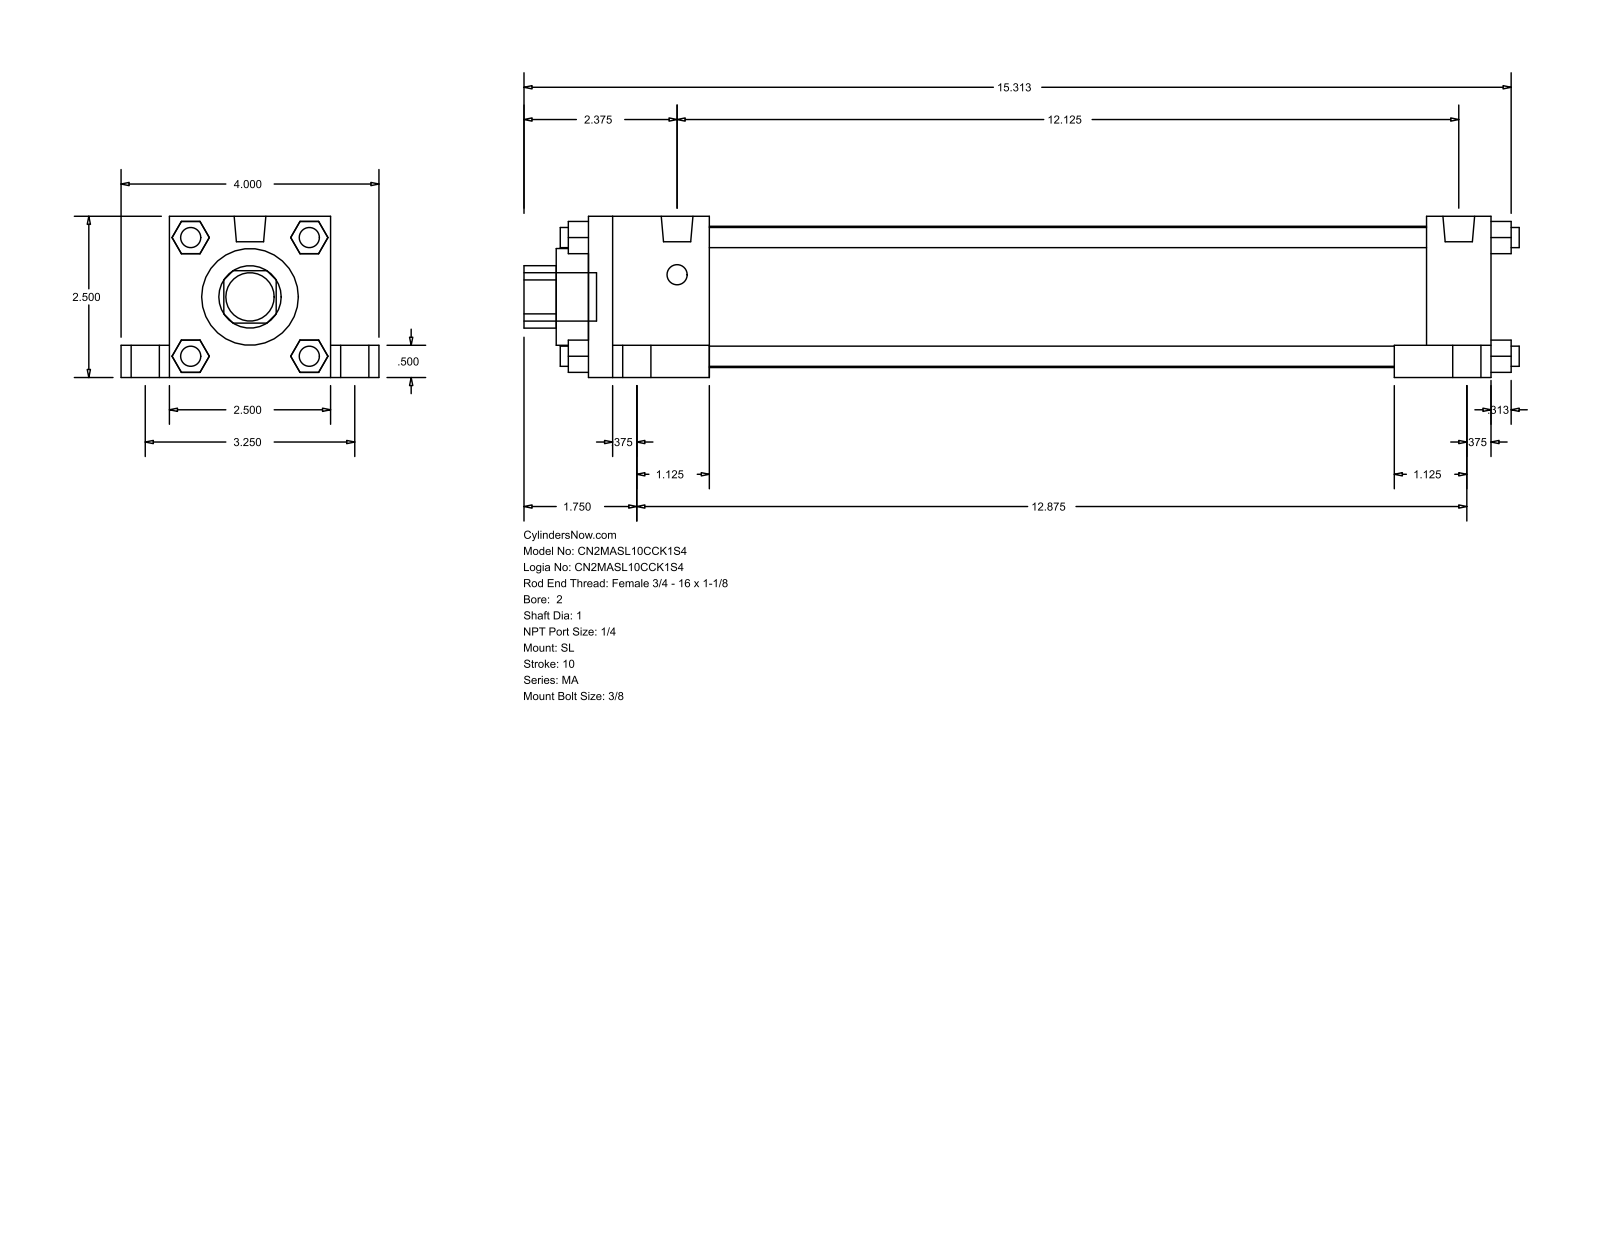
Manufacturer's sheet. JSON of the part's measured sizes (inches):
{"part_name": "MA_SL__0200_1", "step_written_by": "GSSL Pune (CONFIG_CONTROL_DESIGN)", "units": "inches", "bodies": {"solids": 0, "faces": 148, "planar": 112, "cylindrical": 36, "other": 0}, "overall_size": [15.437, 4, 2.5], "round_holes": [[1, 1], [1.5, 1], [2.19, 1]], "round_bosses_or_shafts": [[0.313, 8], [0.687, 4], [0.437, 4], [0.492, 2], [0.75, 1]], "partial_cylinders_radius": [[0.484, 1]], "face_to_face_distances": [2.5, 0.5, 14, 0.75, 3.25, 1, 2, 1.875, 12.125, 13]}
